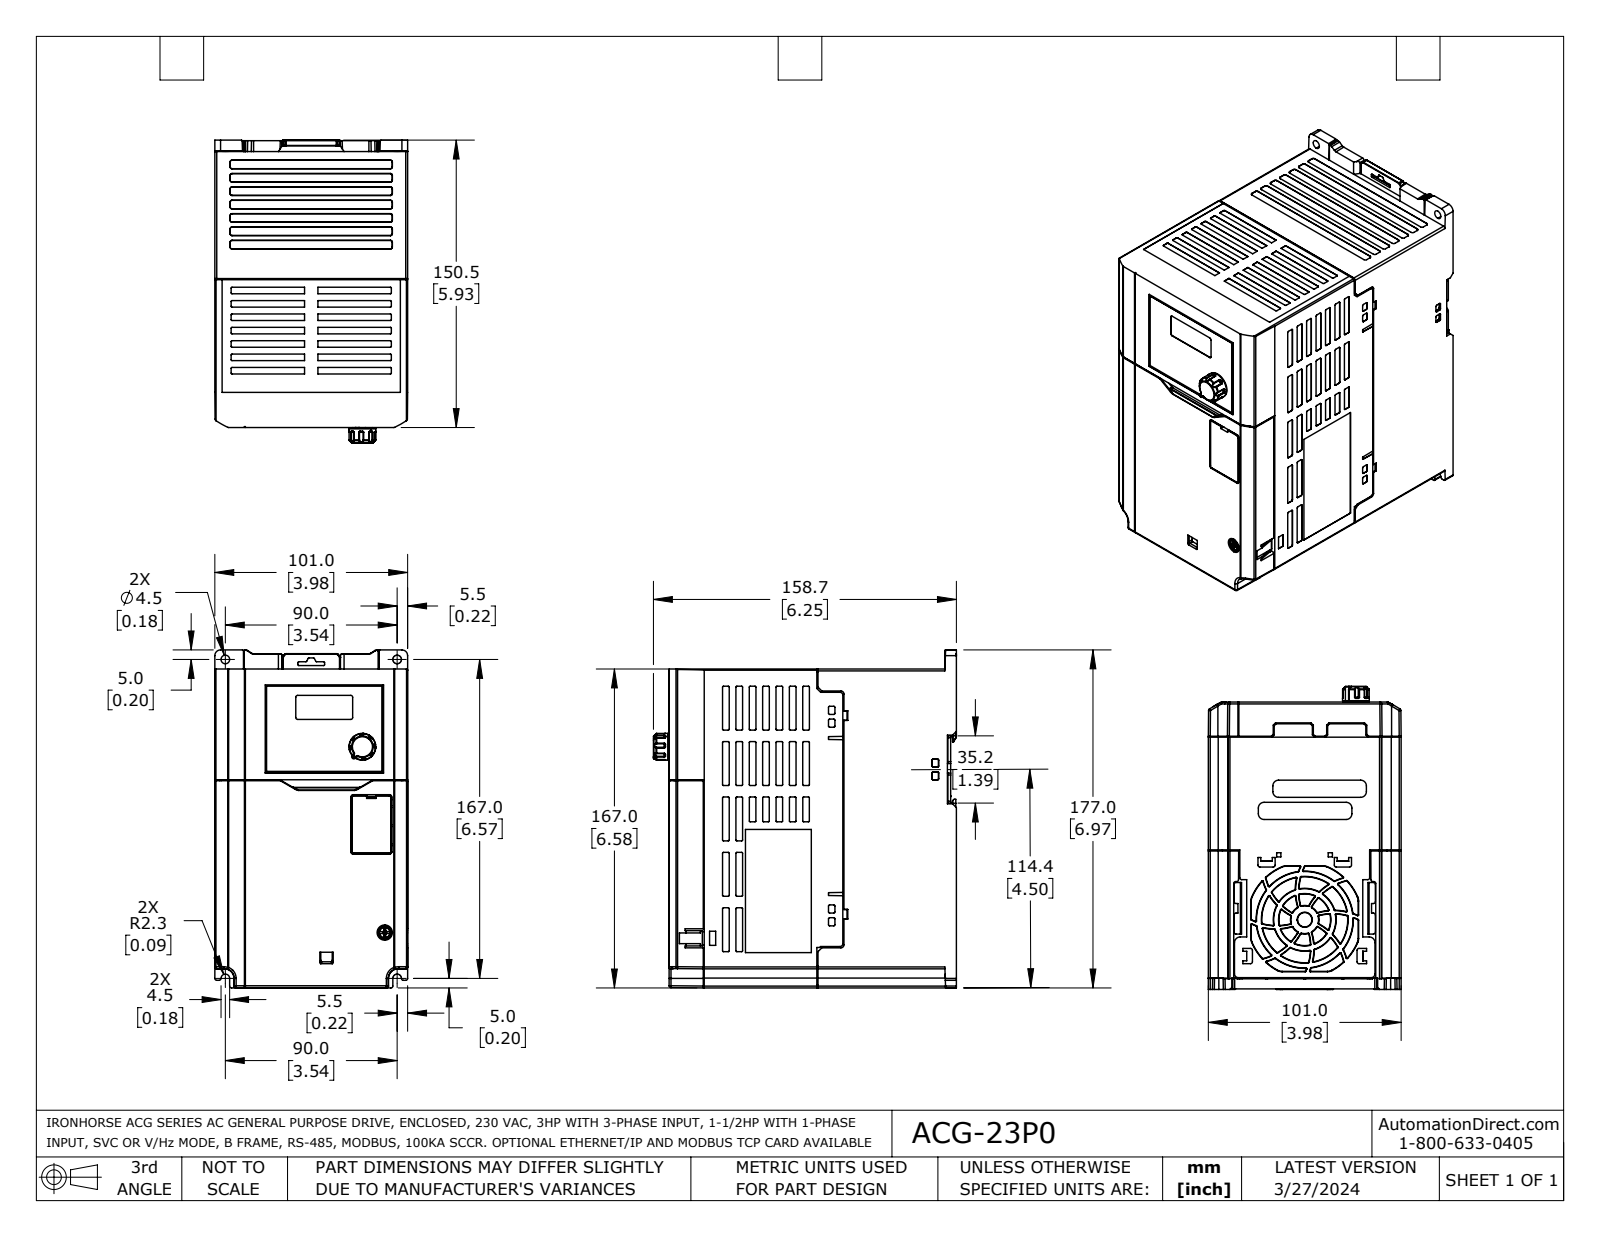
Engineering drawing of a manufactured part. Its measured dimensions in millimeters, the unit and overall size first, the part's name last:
Units: millimetres
Overall size (bounding box): 177 × 158.7 × 101
Round holes (diameter × count): ⌀3.4 ×4, ⌀1 ×1, ⌀7 ×1, ⌀12 ×1
Round bosses / shafts (diameter × count): ⌀14 ×1, ⌀13.8 ×1, ⌀6 ×1
Partial cylindrical surfaces — rounded edges, fillets, slot ends (radius × count): R0.2 ×347, R0.5 ×240, R1 ×95, R0.5 ×38, R0.3 ×24, R0.8 ×17, R3 ×12, R0.4 ×4
Main face-to-face distances: 101, 147.5, 101, 167, 147.2, 167, 2.7, 150.2, 3, 2.5
Hole centre spacings: 88.8, 124, 152.5, 7, 12.5, 23.6, 30.5, 70
Volume: 2 466 000 mm³ · Surface area: 151 300 mm²
Bodies: 4 solids, 4588 faces (1880 planar, 1198 cylindrical, 1510 other)
Part name (STEP PRODUCT): ACG-23P0
STEP written by: SolidWorks 2021 (AUTOMOTIVE_DESIGN)
